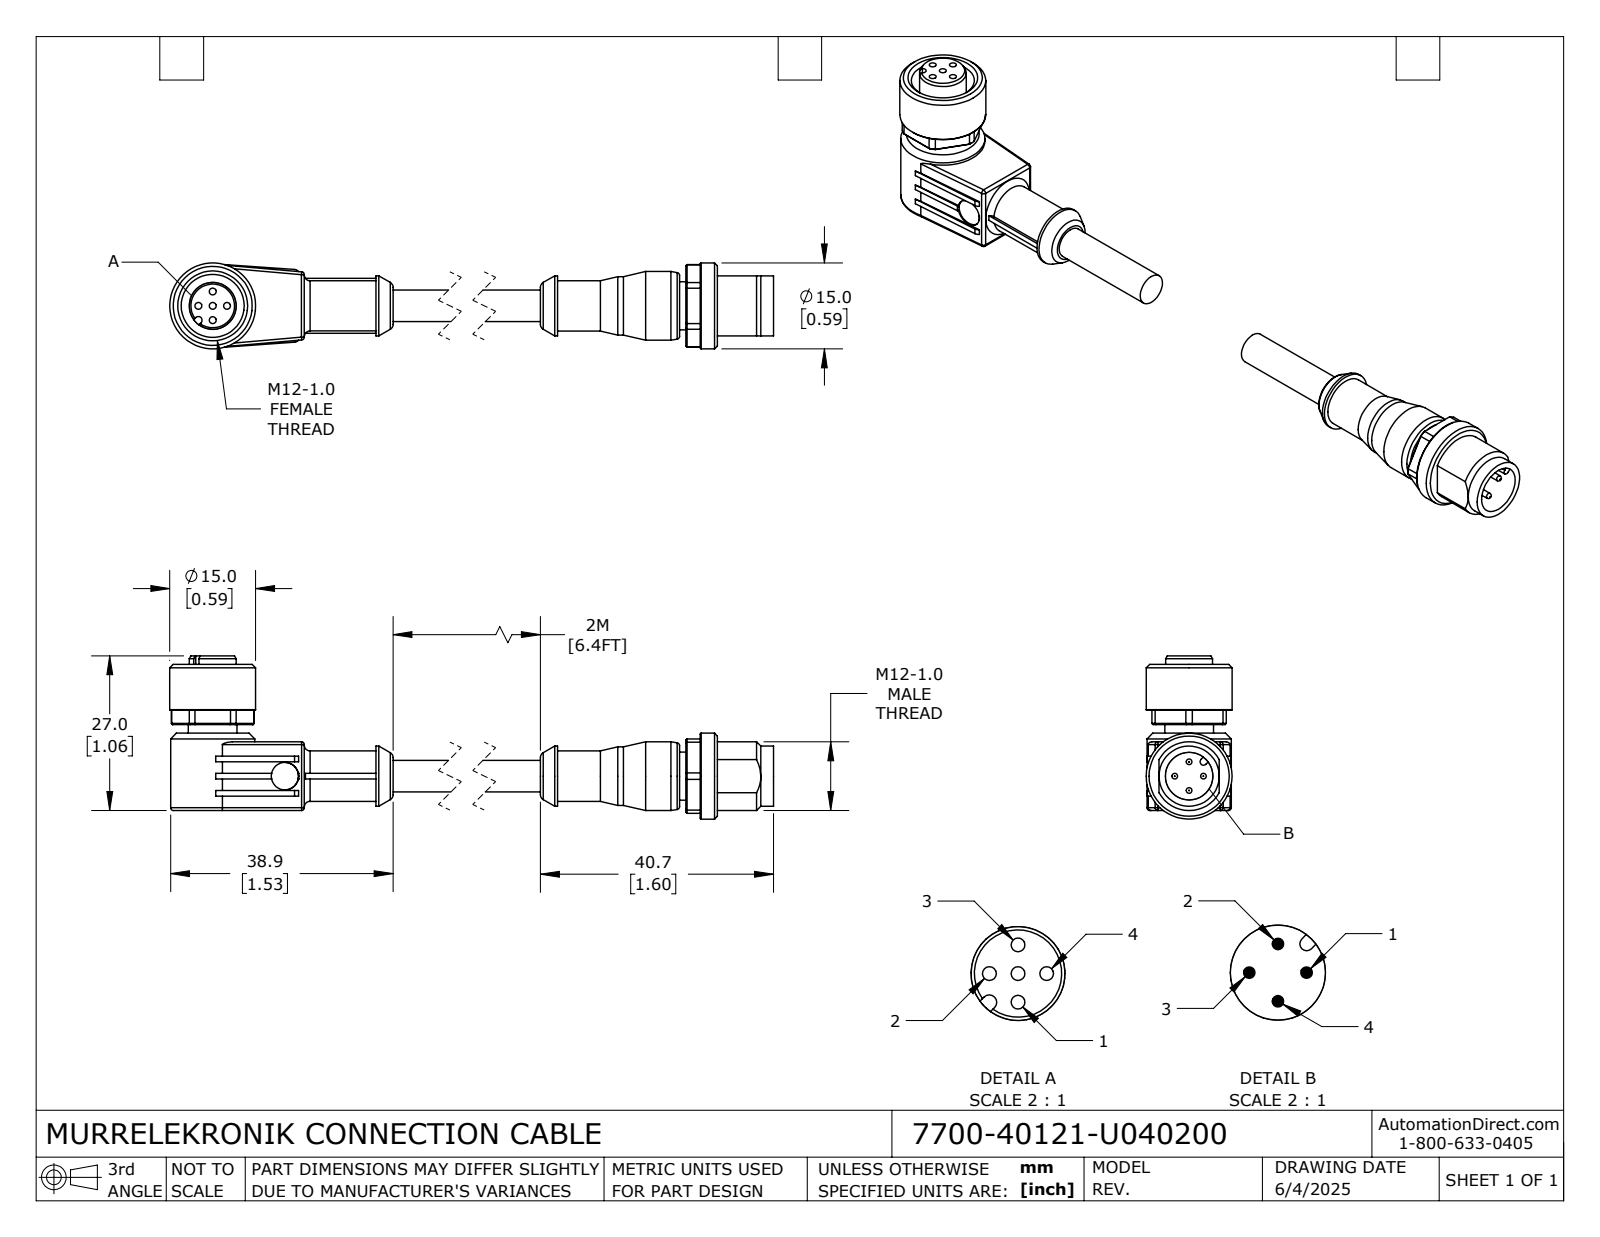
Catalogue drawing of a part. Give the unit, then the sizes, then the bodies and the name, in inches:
Units: inches
Overall size (bounding box): 5.697 × 1.122 × 0.591
Round holes (diameter × count): ⌀0.047 ×5, ⌀0.189 ×1, ⌀0.327 ×1, ⌀0.433 ×1
Round bosses / shafts (diameter × count): ⌀0.039 ×4, ⌀0.591 ×2, ⌀0.579 ×1, ⌀0.472 ×1, ⌀0.413 ×1, ⌀0.402 ×1, ⌀0.346 ×1, ⌀0.335 ×1
Partial cylindrical surfaces — rounded edges, fillets, slot ends (radius × count): R0.02 ×8, R0.039 ×2, R0.283 ×2, R0.024 ×1, R0.026 ×1
Main face-to-face distances: 0.118, 0.472, 0.059, 0.531, 0.217, 0.591, 0.512, 0.236, 0.413, 0.098
Hole centre spacings: 0.098, 0.139, 0.197
Volume: 0.657 in³ · Surface area: 9.438 in²
Bodies: 2 solids, 248 faces (91 planar, 95 cylindrical, 62 other)
Part name (STEP PRODUCT): 7700-40121-U040200_FEMALE; 7700-40121-U040200; 7700-40121-U040200_MALE
STEP written by: SolidWorks 2024 (CONFIG_CONTROL_DESIGN)
